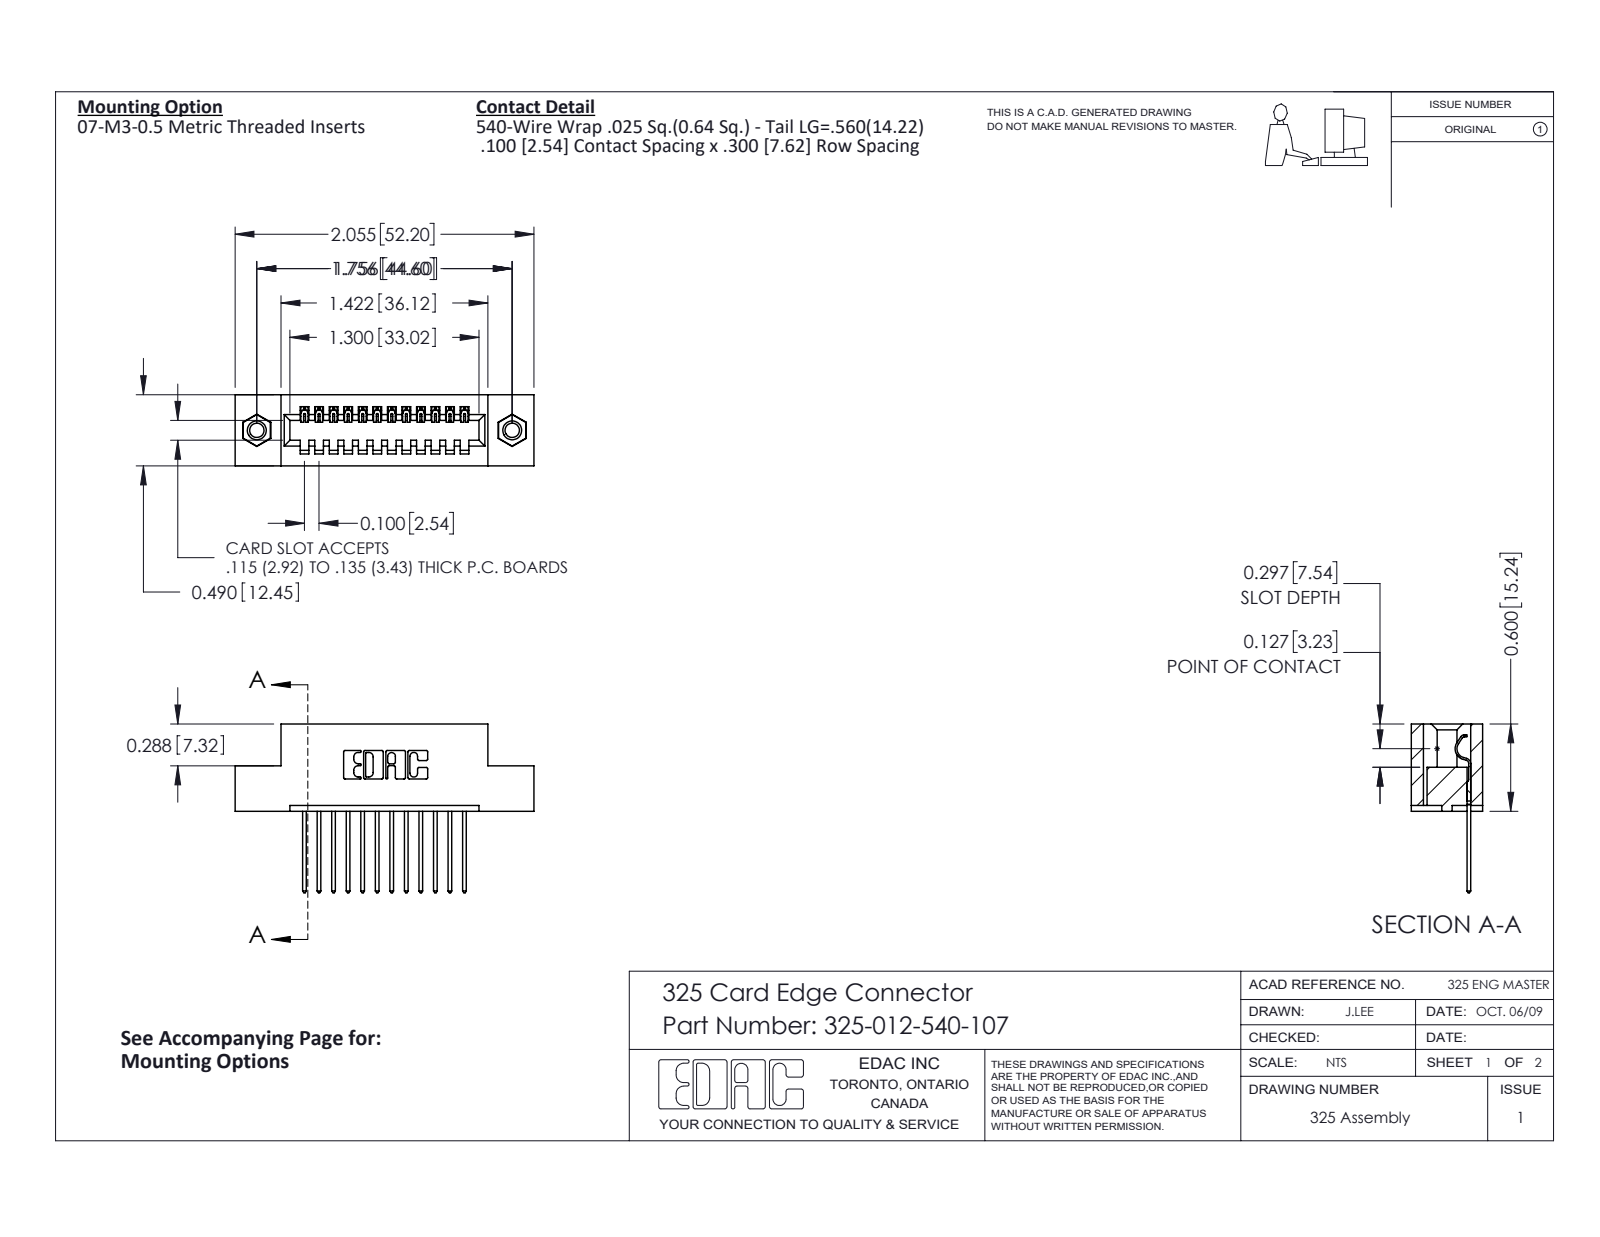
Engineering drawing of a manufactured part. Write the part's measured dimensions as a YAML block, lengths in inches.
part_name: "325 Part_TI; 345-250-001_345-250-005-103; 325-292-001_325-293-140; 325-012-540-107"
step_written_by: "SolidWorks 2016 (CONFIG_CONTROL_DESIGN)"
units: inches
bodies: {solids: 15, faces: 870, planar: 606, cylindrical: 248, other: 16}
overall_size: [2.055, 1.16, 0.49]
volume: 0.39
surface_area: 10.27
round_holes:
  - {diameter: 0.098, count: 2}
  - {diameter: 0.125, count: 2}
  - {diameter: 0.16, count: 2}
round_bosses_or_shafts:
  - {diameter: 0.155, count: 2}
partial_cylinders:
  - {radius: 0.006, count: 24}
  - {radius: 0.01, count: 24}
  - {radius: 0.01, count: 22}
  - {radius: 0.007, count: 6}
  - {radius: 0.031, count: 6}
  - {radius: 0.026, count: 3}
  - {radius: 0.014, count: 1}
  - {radius: 0.022, count: 1}
face_to_face_distances: [0.083, 0.407, 0.3, 0.49, 0.04, 0.1, 0.2, 0.6, 0.107, 0.383]
hole_center_spacings: [1.756]
